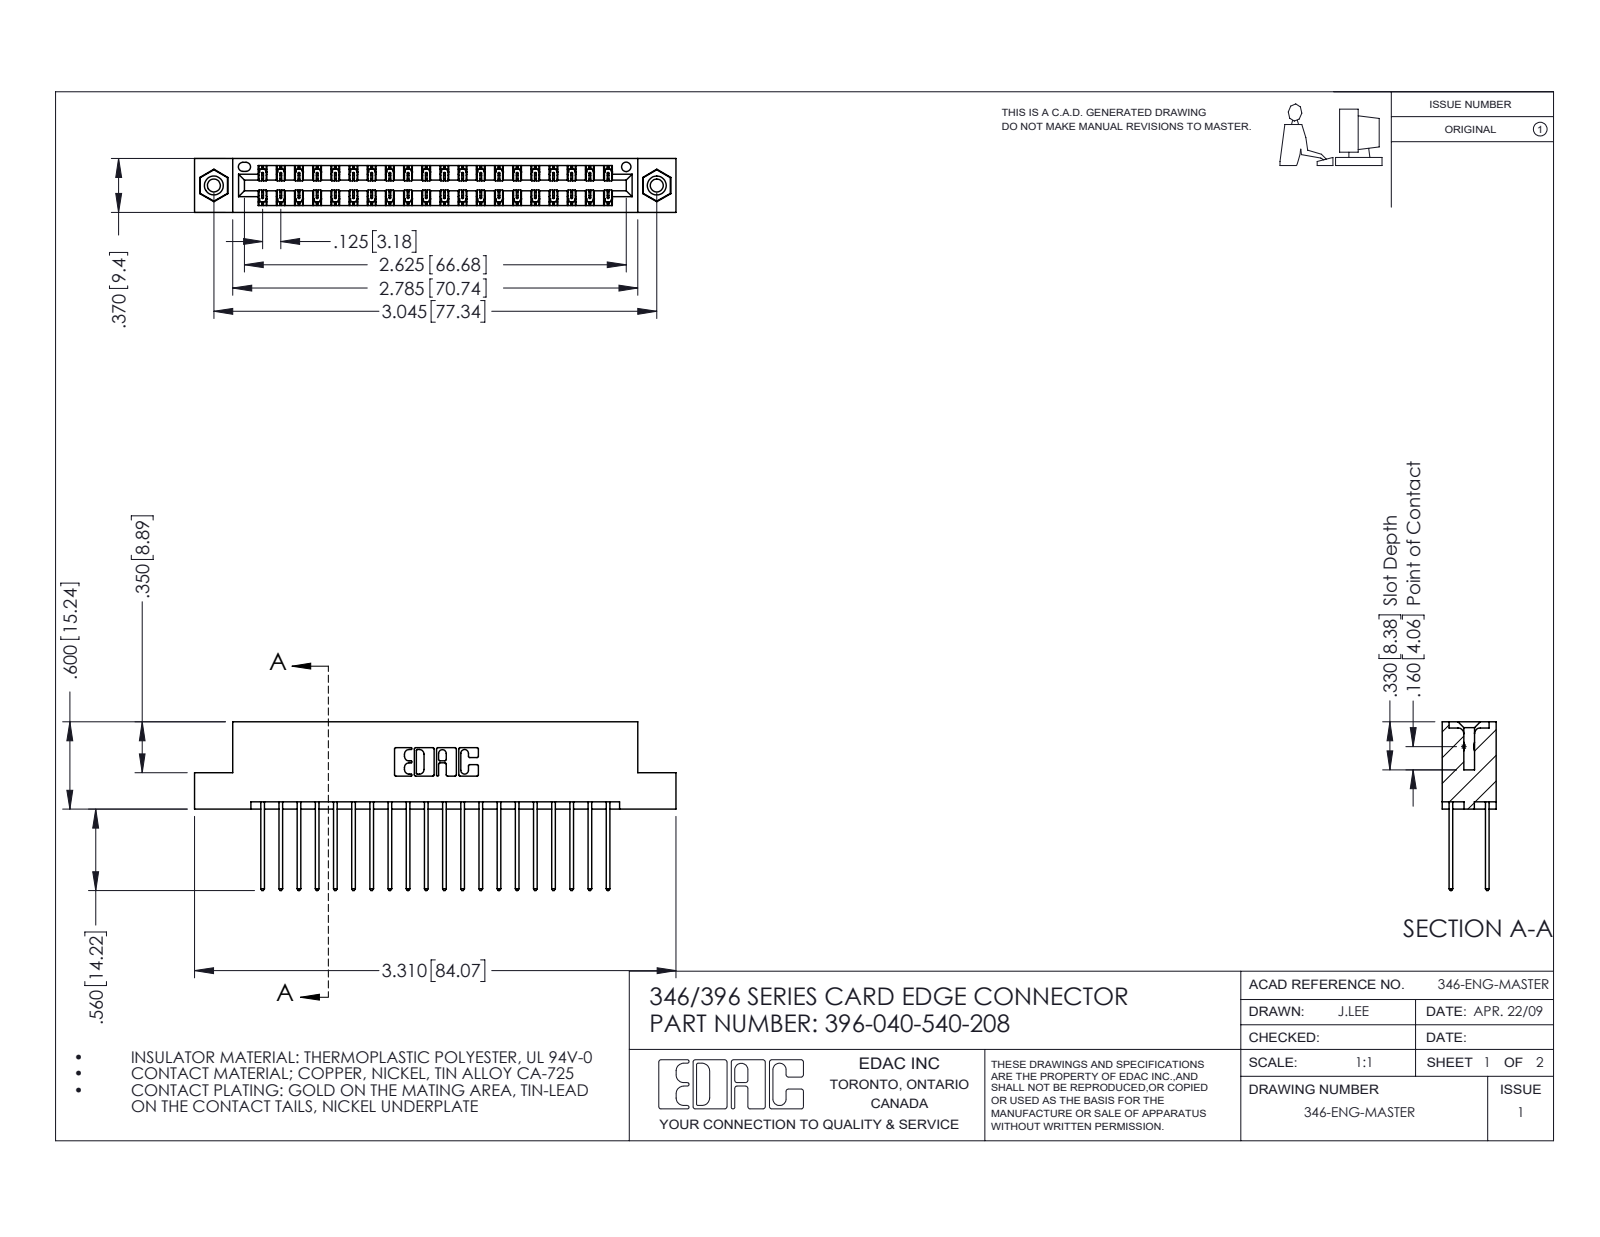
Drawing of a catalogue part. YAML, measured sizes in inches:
part_name: "345-292-001_345-293-140; 345-250-001_345-250-003-102; 396-040-540-208; 346 Part_Flush Mounting Lugs - 0.156 Dia-TI"
step_written_by: "SolidWorks 2016 (CONFIG_CONTROL_DESIGN)"
units: inches
bodies: {solids: 43, faces: 2262, planar: 1508, cylindrical: 738, other: 16}
overall_size: [3.31, 1.16, 0.37]
volume: 0.499
surface_area: 18.02
round_holes:
  - {diameter: 0.089, count: 2}
  - {diameter: 0.125, count: 2}
  - {diameter: 0.156, count: 2}
  - {diameter: 0.064, count: 1}
round_bosses_or_shafts:
  - {diameter: 0.155, count: 2}
partial_cylinders:
  - {radius: 0.006, count: 60}
  - {radius: 0.01, count: 40}
  - {radius: 0.01, count: 22}
  - {radius: 0.007, count: 6}
  - {radius: 0.031, count: 6}
  - {radius: 0.026, count: 3}
  - {radius: 0.014, count: 2}
  - {radius: 0.022, count: 2}
face_to_face_distances: [0.048, 0.322, 0.25, 0.37, 0.072, 0.298, 0.025, 0.275, 0.148, 0.222]
hole_center_spacings: [0.246, 2.837, 3.045]
